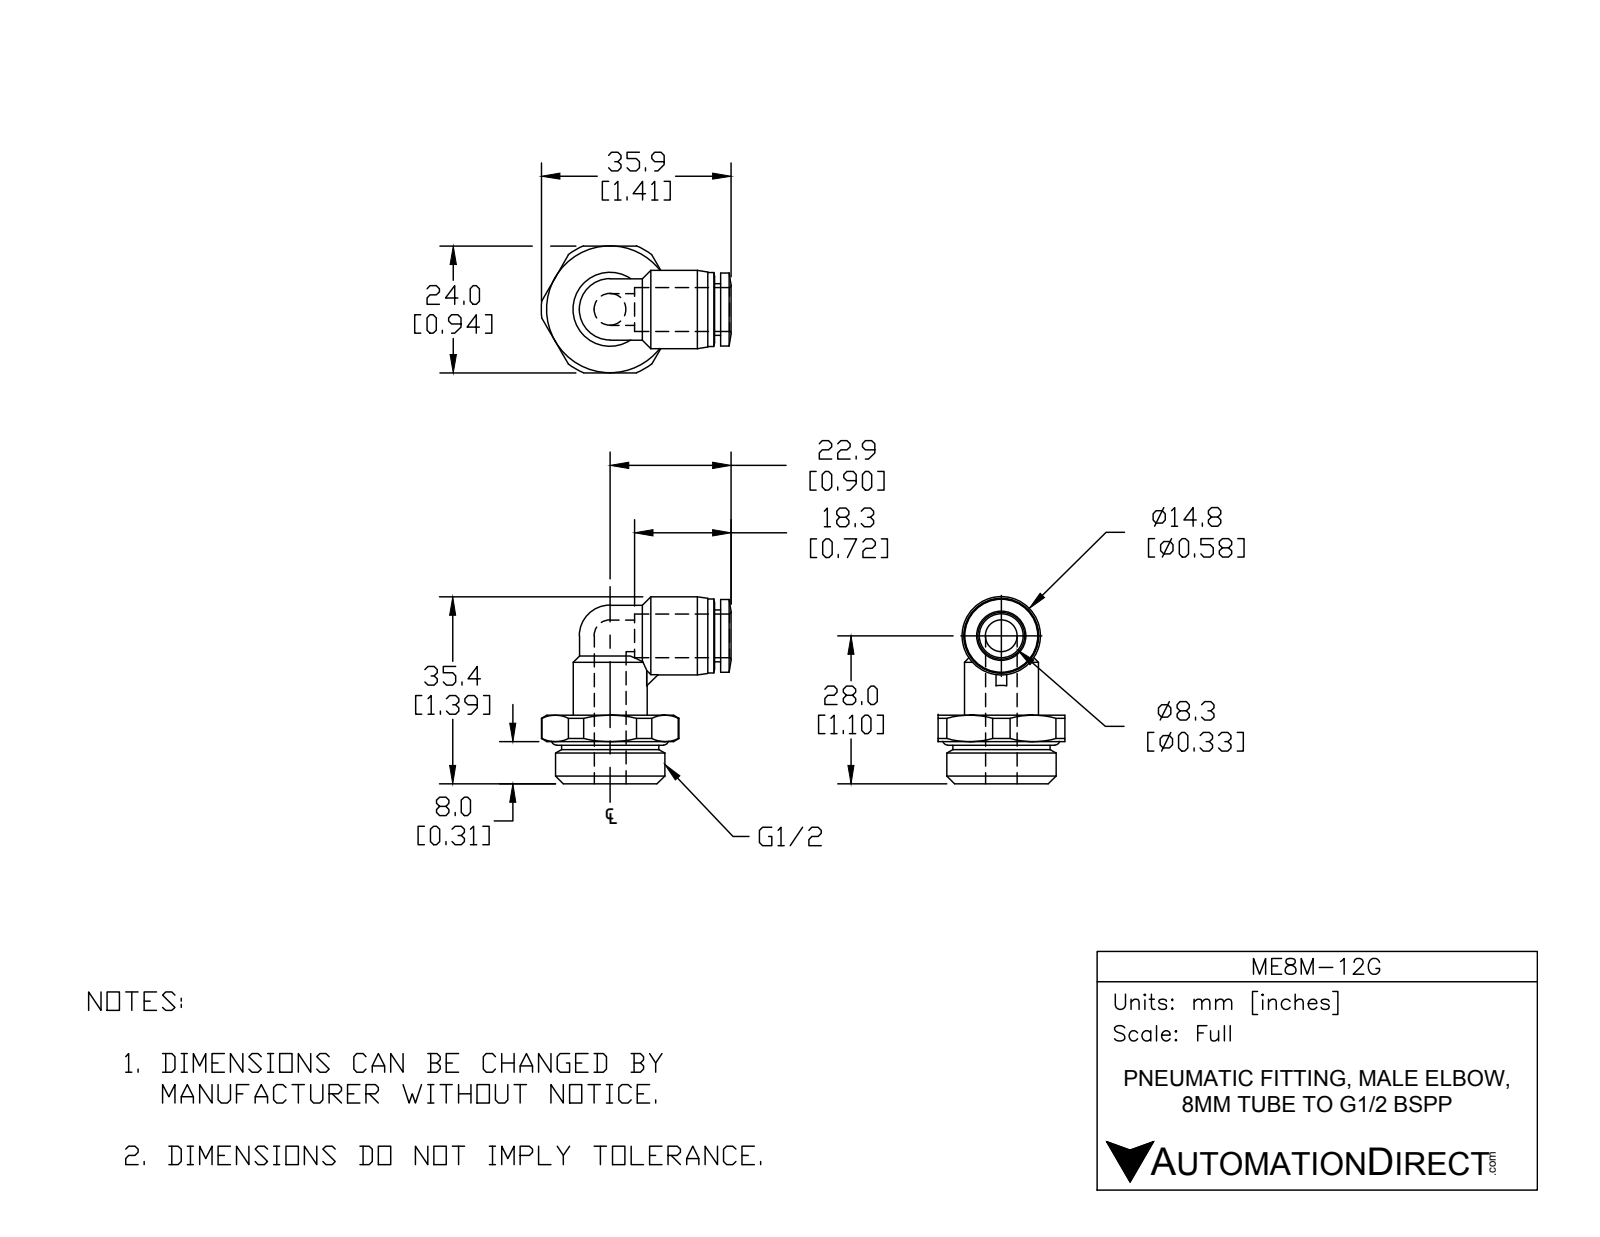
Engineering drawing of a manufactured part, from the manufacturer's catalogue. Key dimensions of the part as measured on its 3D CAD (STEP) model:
Part name (STEP PRODUCT): ME8M-12G
STEP written by: SolidWorks 2018 (AUTOMOTIVE_DESIGN)
Units: inches
Bodies: 2 solids, 85 faces (18 planar, 29 cylindrical, 38 other)
Overall size (bounding box): 1.413 × 1.394 × 0.945
Volume: 0.512 in³ · Surface area: 7.936 in²
Round holes (diameter × count): ⌀0.236 ×2, ⌀0.327 ×1
Round bosses / shafts (diameter × count): ⌀0.551 ×2, ⌀0.815 ×1, ⌀0.724 ×1, ⌀0.583 ×1, ⌀0.543 ×1, ⌀0.457 ×1, ⌀0.386 ×1
Partial cylindrical surfaces — rounded edges, fillets, slot ends (radius × count): R0.228 ×1, R0.512 ×1
Main face-to-face distances: 0.512, 0.945, 0.045, 0.315, 0.197, 0.362, 0.047, 0.15, 0.596, 0.642
